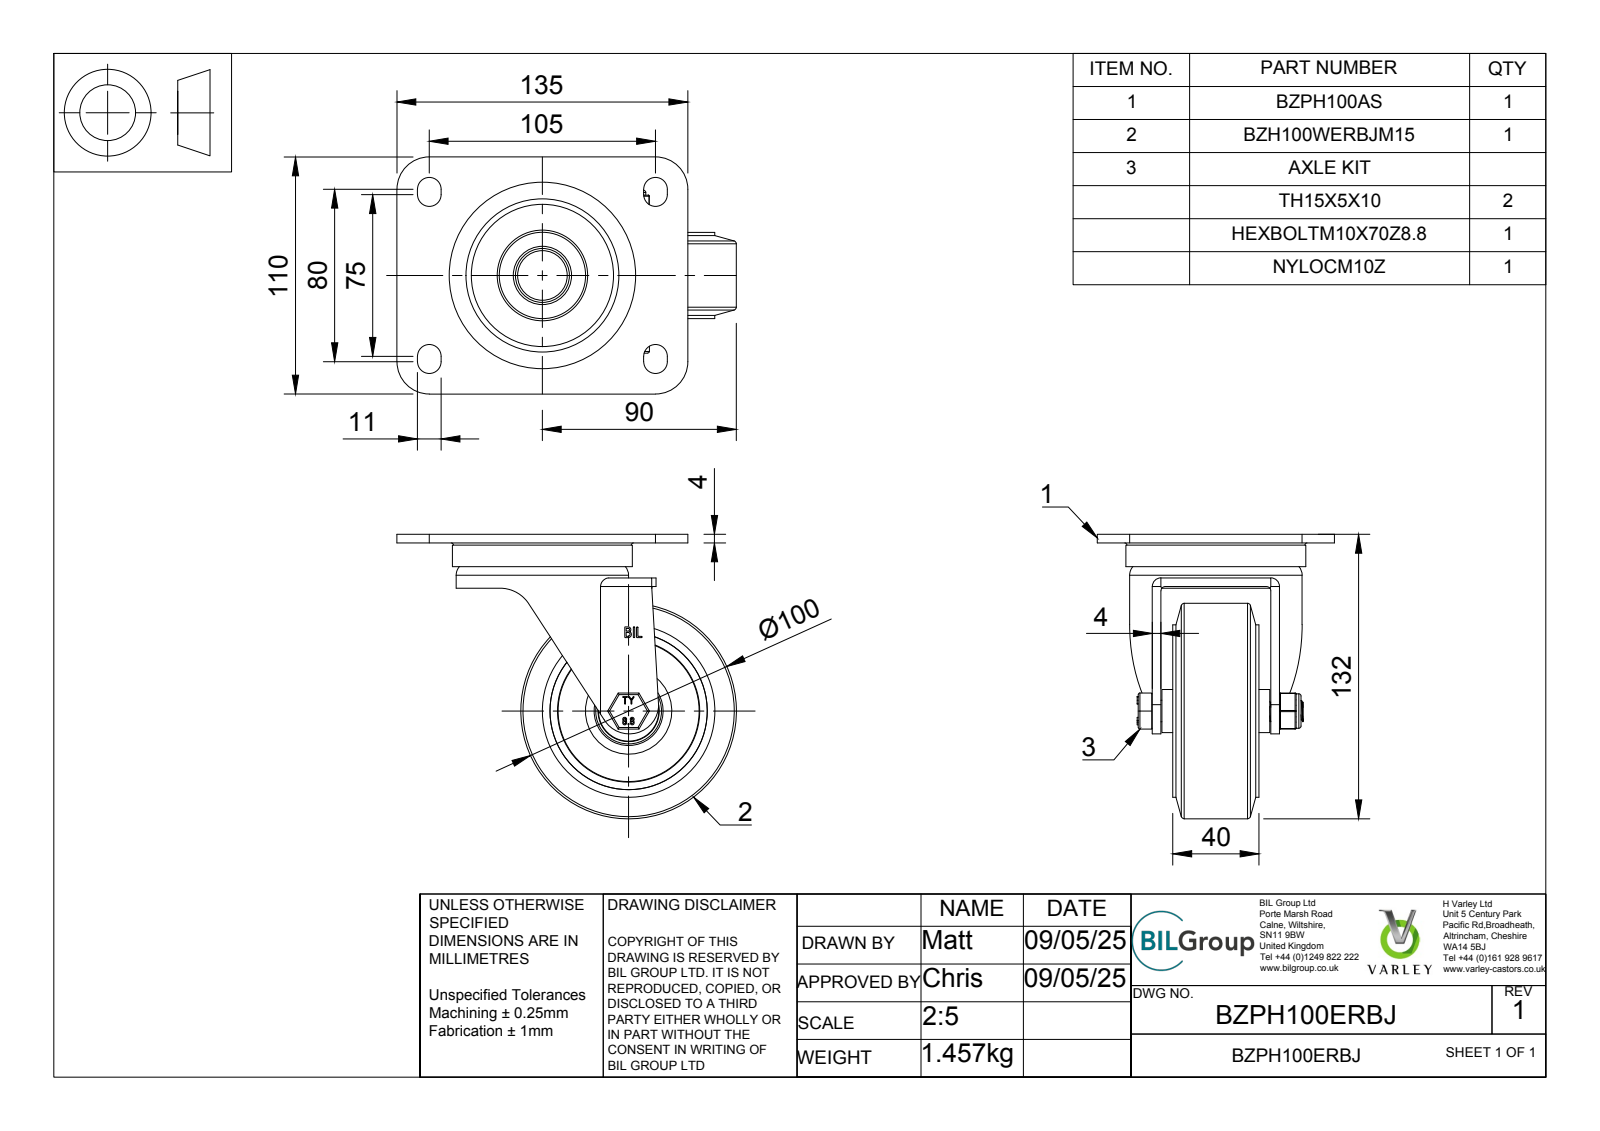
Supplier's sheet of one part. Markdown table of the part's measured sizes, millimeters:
| quantity | value |
| --- | --- |
| part name | BZPH100ERBJ v3; BZPH100AS v1; ZINC PLATED, PRESSED STEEL TOP PLATE; ZINC PLATED, PRESSED STEEL FORKS (+8 more) |
| STEP written by | Autodesk Translation Framework v14.4.0.0 (AUTOMOTIVE_DESIGN) |
| units | millimeters |
| bodies | 40 solids, 1112 faces (499 planar, 196 cylindrical, 417 other) |
| overall size | 157.5 × 132 × 110 |
| volume | 376 253 mm³ |
| surface area | 157 136 mm² |
| round holes (diameter × count) | 10 × 1, 10.2 × 1, 10.5 × 1, 12 × 1, 15 × 1, 18 × 1, 20 × 1, 21 × 1, 26 × 1, 27.4 × 1, 28 × 1, 32 × 1 |
| round bosses / shafts (diameter × count) | 80 × 2, 100 × 1, 83.5 × 1, 51 × 1, 40 × 1, 32 × 1, 28.4 × 1, 28 × 1 |
| partial cylindrical surfaces (radius × count) | 0.5 × 18, 5.5 × 8, 0.75 × 6, 2 × 4, 15 × 4, 4 × 2, 11.47 × 1, 13.47 × 1 |
| main face-to-face distances | 4, 9, 13, 16, 8, 24, 25.5, 29.5, 9.5, 33.5 |
